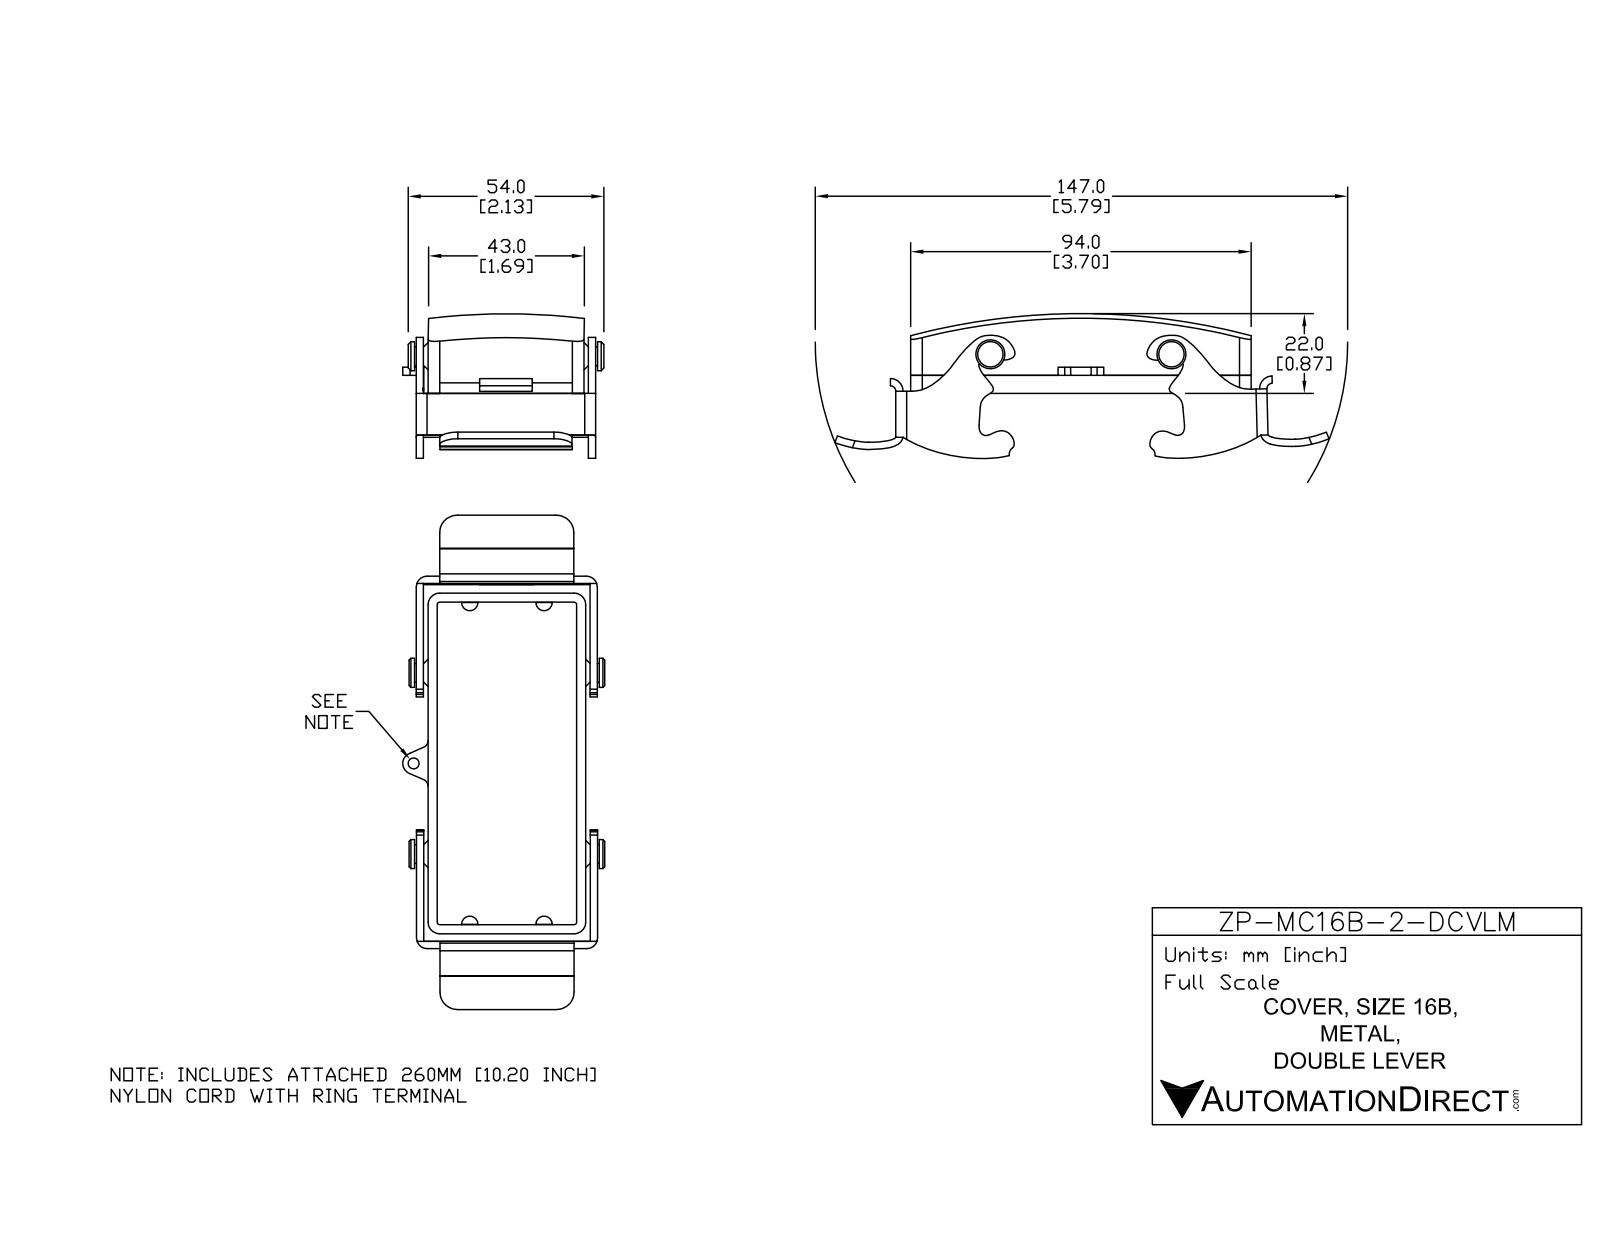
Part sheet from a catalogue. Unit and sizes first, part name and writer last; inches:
Units: inches
Overall size (bounding box): 4.979 × 2.195 × 1.776
Round holes (diameter × count): ⌀0.118 ×1
Round bosses / shafts (diameter × count): ⌀0.315 ×2, ⌀0.204 ×2
Partial cylindrical surfaces — rounded edges, fillets, slot ends (radius × count): R0.039 ×12, R0.02 ×10, R0.079 ×8, R0.157 ×6, R0.028 ×4, R0.03 ×4, R0.089 ×4, R0.126 ×4
Main face-to-face distances: 0.098, 0.039, 1.614, 0.148, 1.762, 0.049, 0.089, 1.663, 0.187, 1.703
Volume: 1.607 in³ · Surface area: 46.59 in²
Bodies: 6 solids, 264 faces (122 planar, 132 cylindrical, 10 other)
Part name (STEP PRODUCT): ZP-MC16B-2-DCVLM
STEP written by: SolidWorks 2011 (AUTOMOTIVE_DESIGN)
